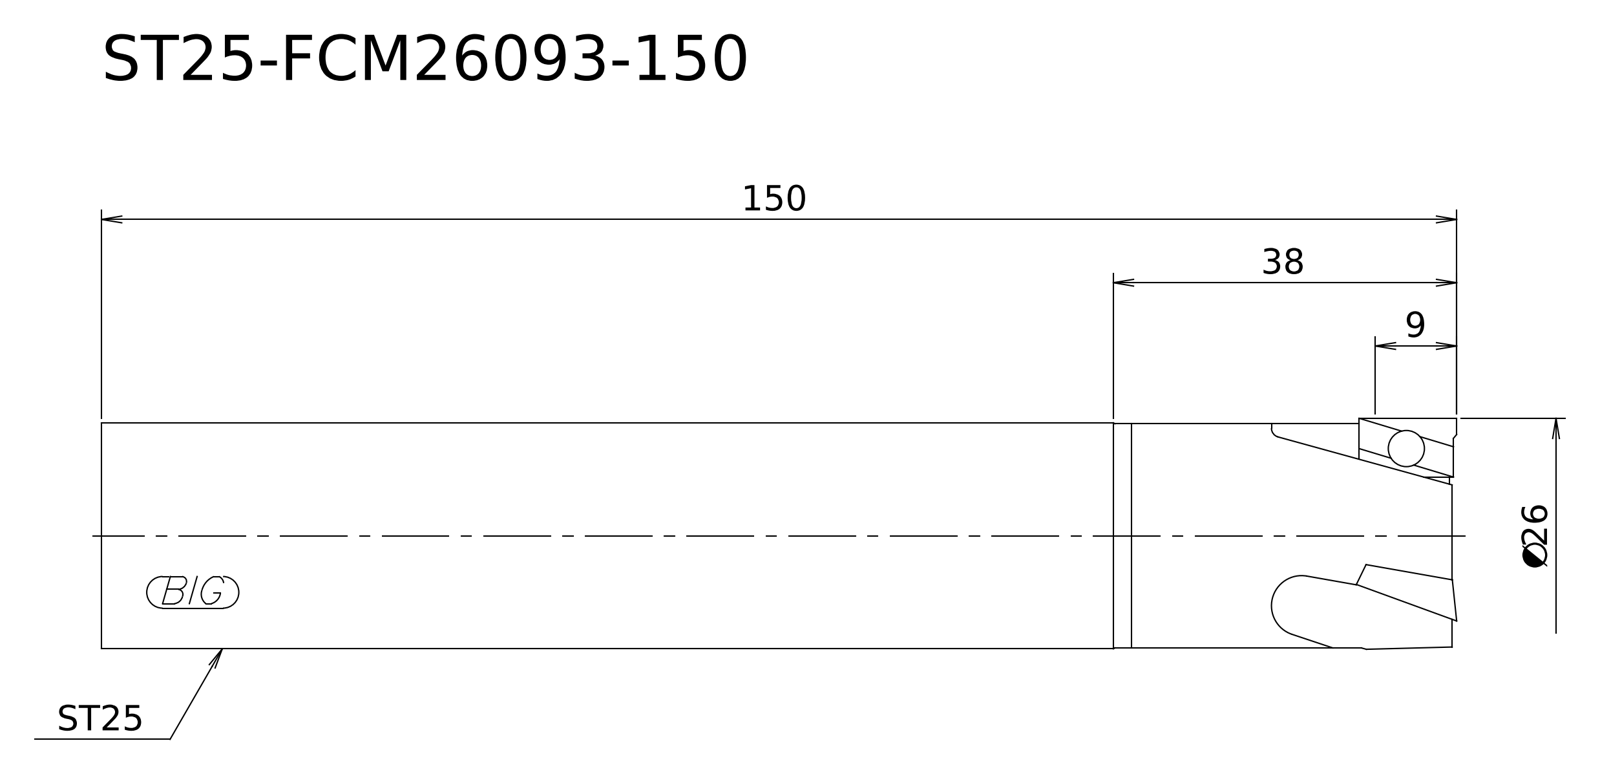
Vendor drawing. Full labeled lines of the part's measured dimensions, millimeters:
STEP written by: Kubotek KeyCreator V8.5.1 (14335) (CONFIG_CONTROL_DESIGN)
Units: millimetres
Bodies: 1 solid, 7 faces (3 planar, 3 cylindrical, 1 other)
Overall size (bounding box): 150 × 26 × 26
Volume: 73 851 mm³ · Surface area: 12 870 mm²
Round bosses / shafts (diameter × count): ⌀26 ×1, ⌀25 ×1, ⌀24.8 ×1
Main face-to-face distances: 150, 10.79, 139.21
